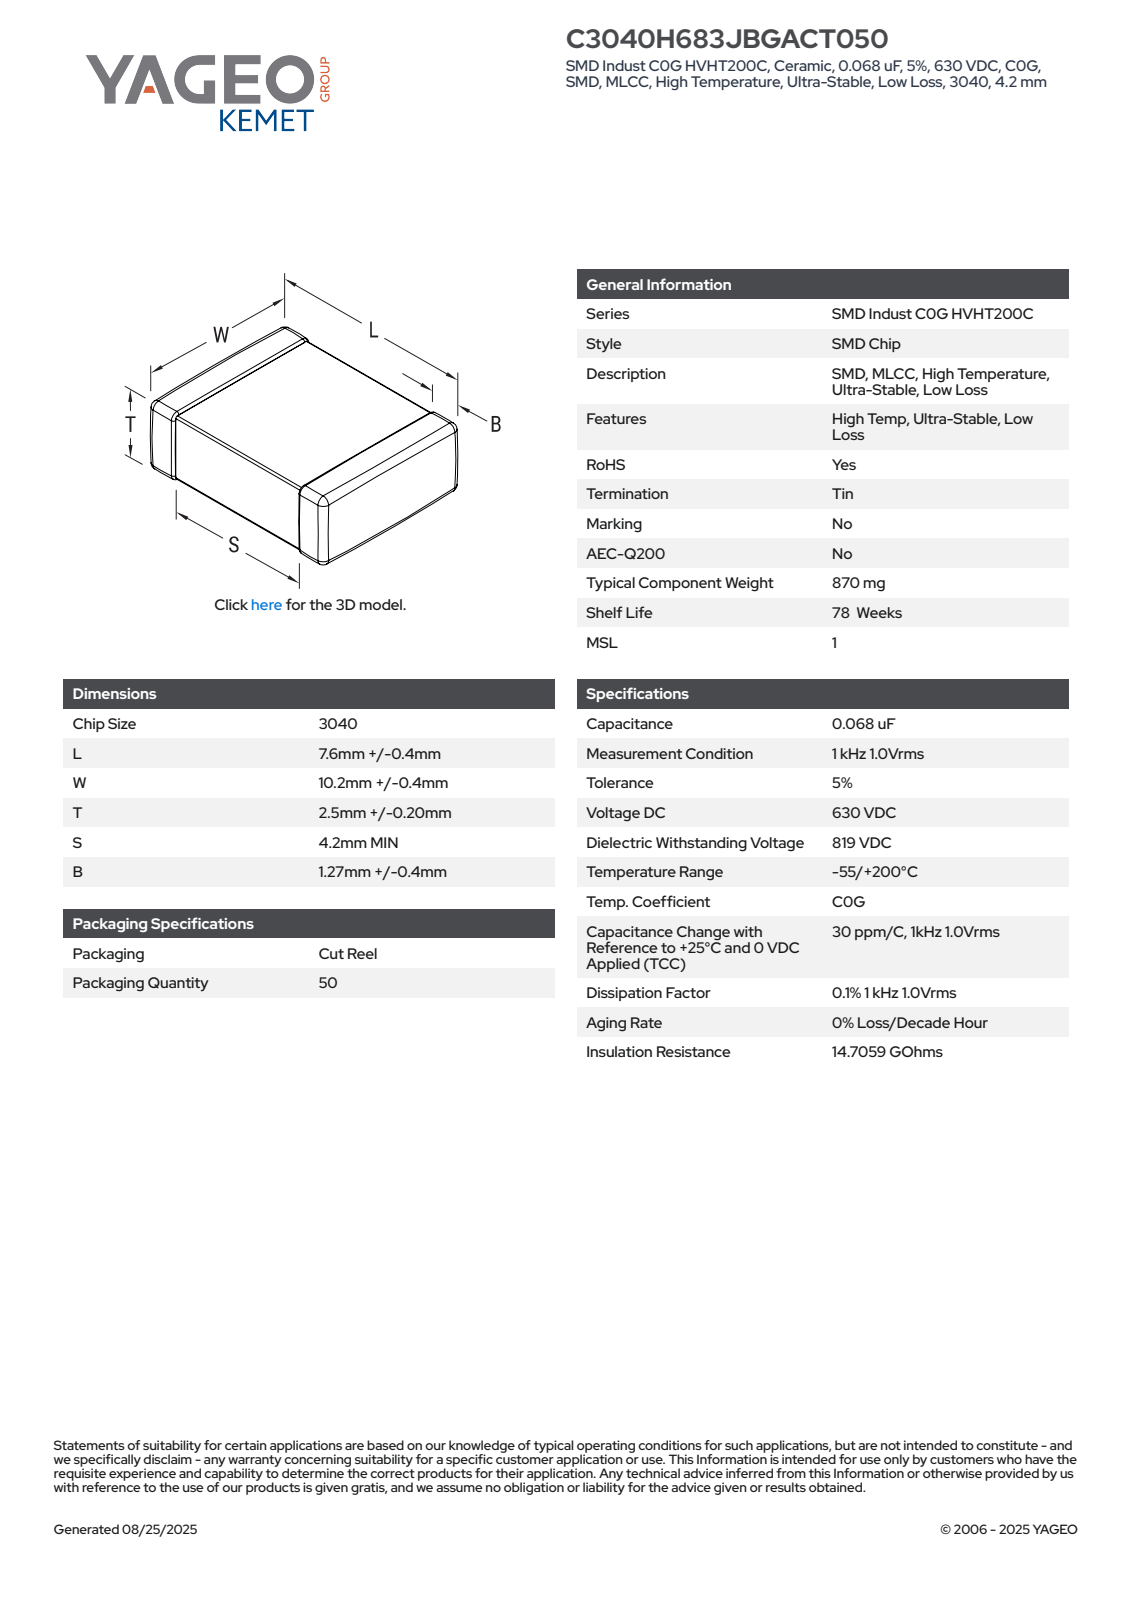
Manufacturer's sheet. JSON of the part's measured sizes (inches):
{"part_name": "CCS_CCSTD_3040_L8W10.6T2.7B1.27", "step_written_by": "SolidWorks 2021 (AUTOMOTIVE_DESIGN)", "units": "inches", "bodies": {"solids": 4, "faces": 125, "planar": 71, "cylindrical": 38, "other": 16}, "overall_size": [0.417, 0.315, 0.106], "volume_in3": 0.012, "surface_area_in2": 0.426, "partial_cylinders_radius": [[0.009, 24]], "face_to_face_distances": [0.098, 0.089, 0.106, 0.315, 0.409, 0.4, 0.417, 0.109, 0.206, 0.17]}
